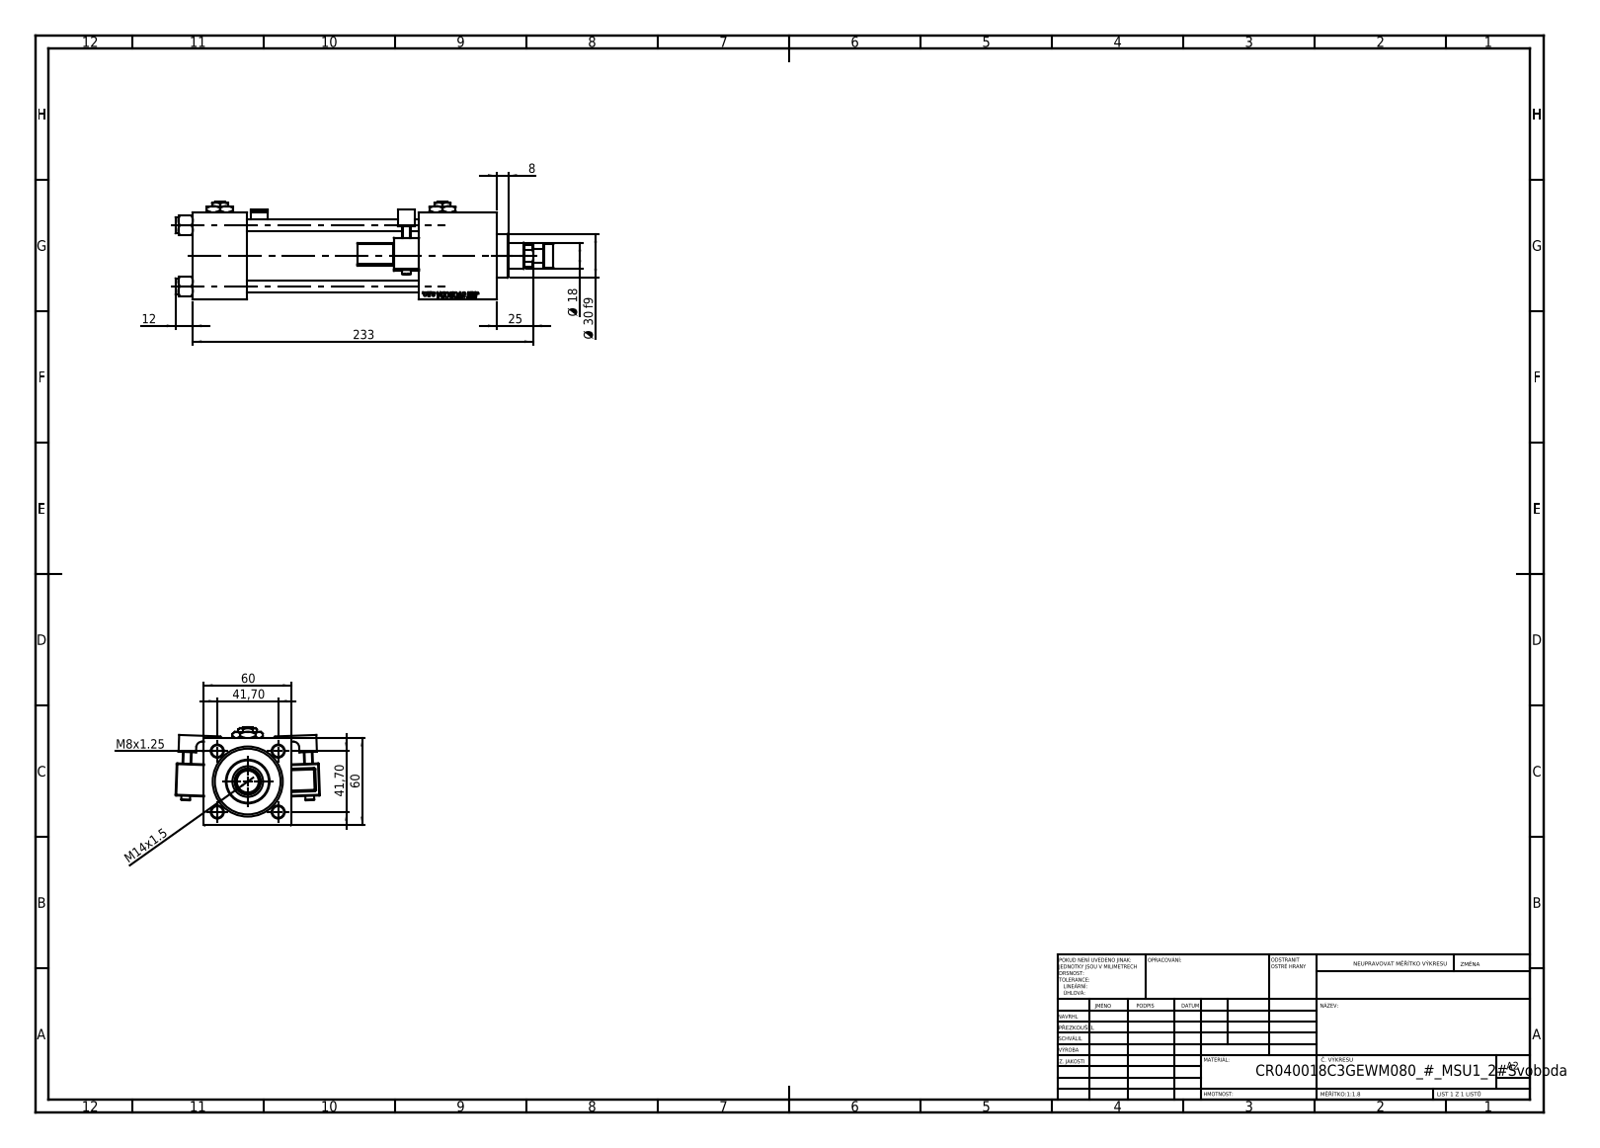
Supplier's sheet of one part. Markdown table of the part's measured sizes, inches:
| quantity | value |
| --- | --- |
| part name | V215CR_ROD_END_W; V215CR_C_Body; NUT_M5_C; V215CR_VCP_C (+4 more) |
| STEP written by | SolidWorks 2019 (CONFIG_CONTROL_DESIGN) |
| units | inches |
| bodies | 16 solids, 1417 faces (635 planar, 162 cylindrical, 620 other) |
| overall size | 10.197 × 3.892 × 2.638 |
| volume | 30.1 in³ |
| surface area | 227.9 in² |
| round holes (diameter × count) | 0.315 × 4, 0.276 × 2, 0.656 × 2, 0.945 × 2, 0.335 × 1, 0.709 × 1, 0.827 × 1, 1.22 × 1, 1.575 × 1, 1.772 × 1 |
| round bosses / shafts (diameter × count) | 0.433 × 4, 0.236 × 2, 1.811 × 1, 1.181 × 1, 0.63 × 1, 0.394 × 1 |
| partial cylindrical surfaces (radius × count) | 0.02 × 48, 0.039 × 2, 0.098 × 2, 0.157 × 2, 0.335 × 1 |
| main face-to-face distances | 2.362, 1.457, 6.102, 4.646, 2.087, 8.189, 6.732, 7.059, 5.602, 0.957 |
| hole center spacings | 1.161, 1.642, 2.322, 6.004 |
